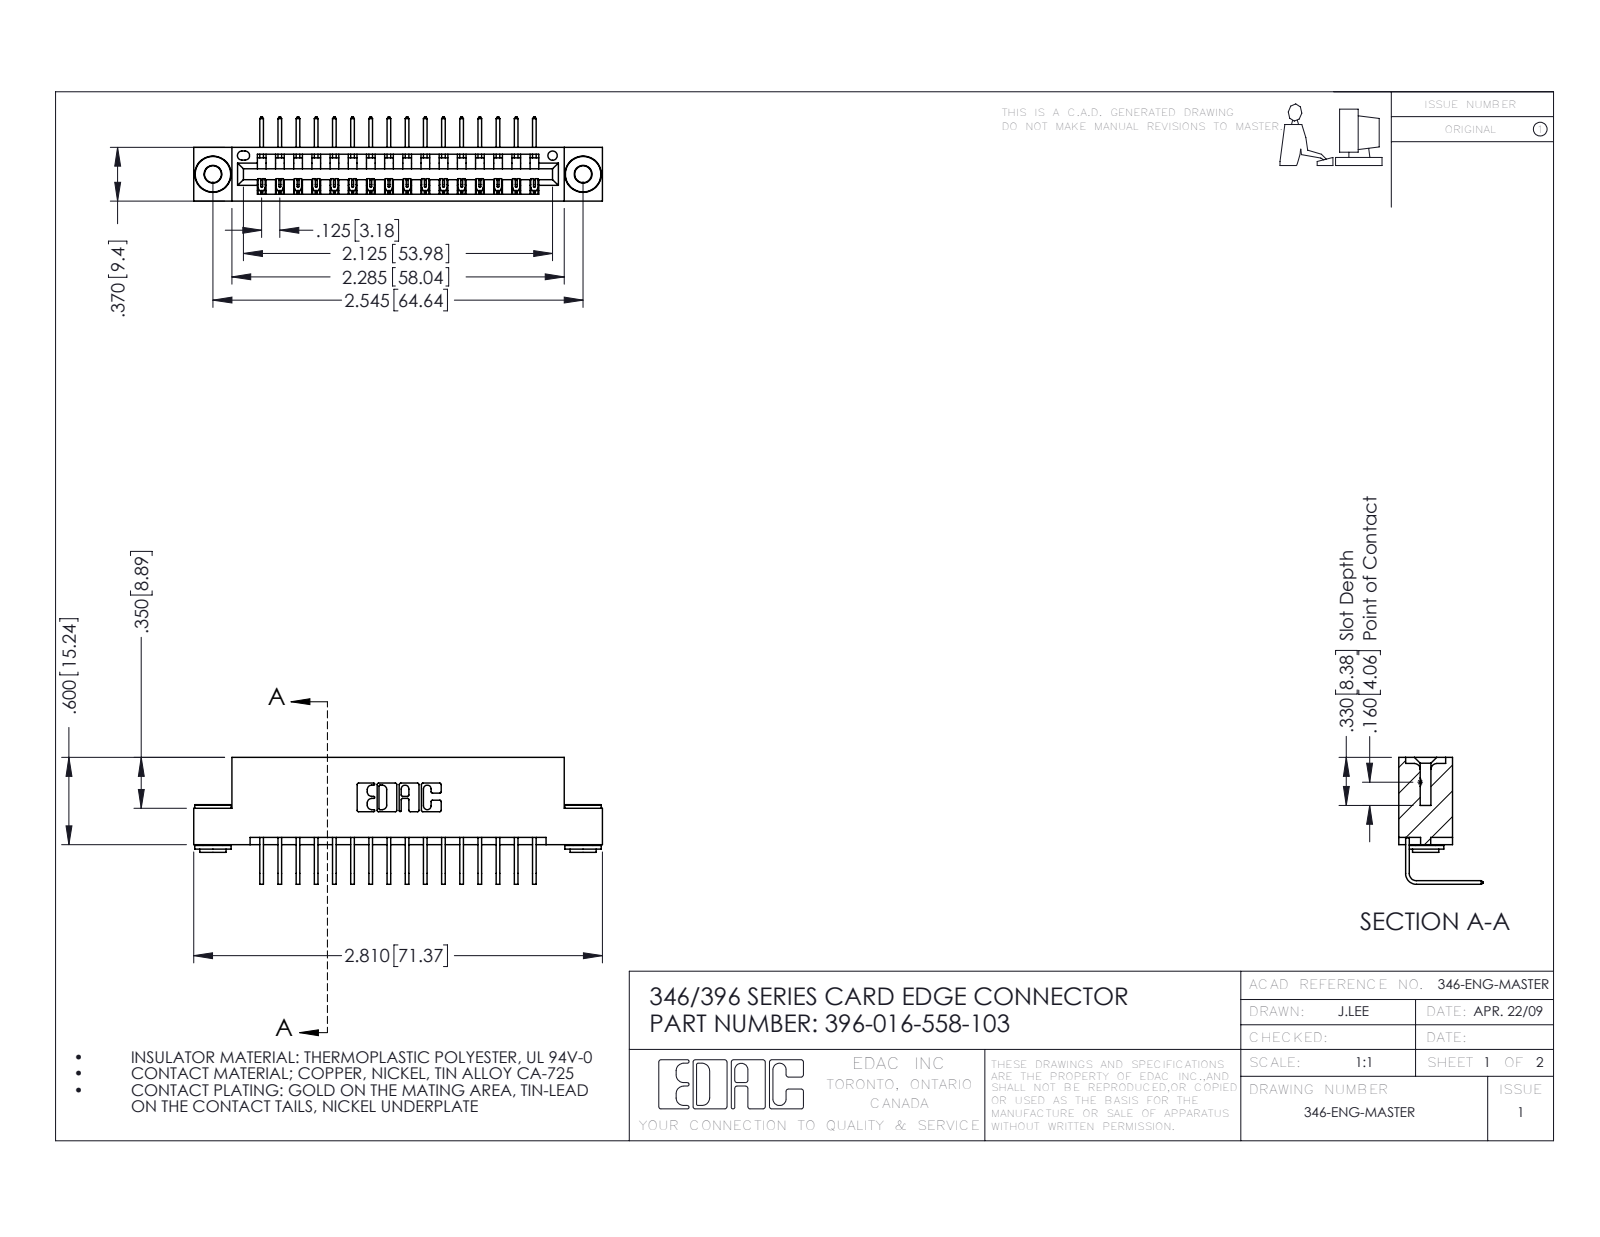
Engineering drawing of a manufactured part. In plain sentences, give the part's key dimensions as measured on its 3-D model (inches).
The part is named "346 Part_Flush Mounting Lugs - 0.156 Dia-TH; 345-250-002_345-250-002-102; 396-016-558-103; 345-292-001_558 Tail - 2". Its 3-D file was written by "SolidWorks 2016 (CONFIG_CONTROL_DESIGN)". It is 19 solids with 1120 faces: 758 planar, 354 cylindrical and 8 other. Overall it measures 2.81 by 0.873 by 0.58 inches. Its volume is 0.41 cubic inches and its surface area 13.43 square inches. Round holes: 2 of diameter 0.116, 2 of diameter 0.156, 1 of diameter 0.064. Round bosses or shafts: 2 of diameter 0.25, 2 of diameter 0.18, 2 of diameter 0.136. Partial cylindrical surfaces (rounded edges, fillets, slot ends): 32 of radius 0.006, 22 of radius 0.01, 6 of radius 0.007, 6 of radius 0.031, 3 of radius 0.026, 2 of radius 0.031, 2 of radius 0.04, 1 of radius 0.014. The main face-to-face distances are 0.322, 0.25, 0.048, 0.37, 0.025, 0.298, 0.072, 0.148, 0.222, 0.1. The hole center spacings are 0.246, 2.338, 2.545.
